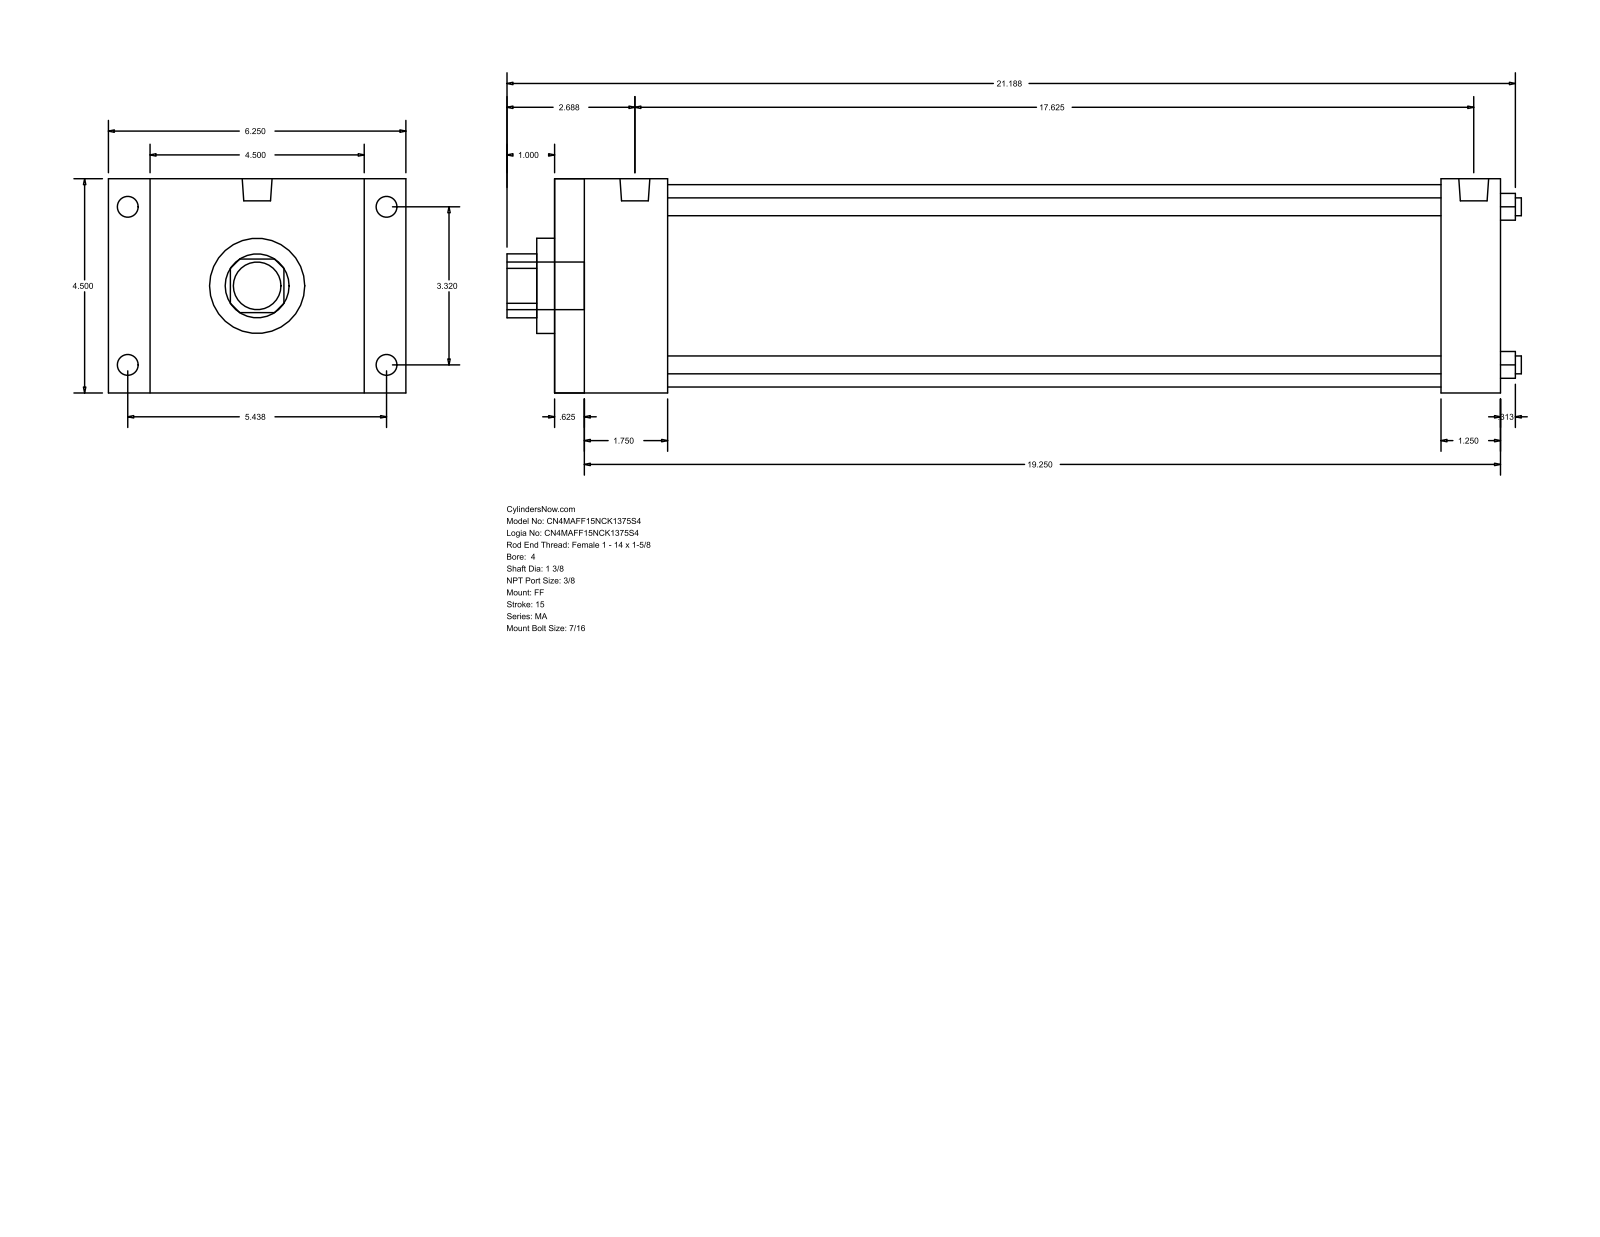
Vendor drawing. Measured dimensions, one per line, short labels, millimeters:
name: MA_FF__0400_1.375
written by: GSSL Pune (CONFIG_CONTROL_DESIGN)
unit: mm
bodies: 0 solids, 92 faces (64 planar, 28 cylindrical, 0 other)
size: 541.34 × 158.75 × 114.3
holes: 4× ⌀9.53, 1× ⌀34.92, 1× ⌀50.8, 1× ⌀107.95
bosses: 8× ⌀11.11, 2× ⌀15.93, 1× ⌀25.4
rounds: 1× R17.06
face distances: 114.3, 504.83, 15.87, 488.96, 22.23, 136.53, 473.08, 457.21, 31.75, 60.32
hole spacings: 59.62, 84.32, 119.25
